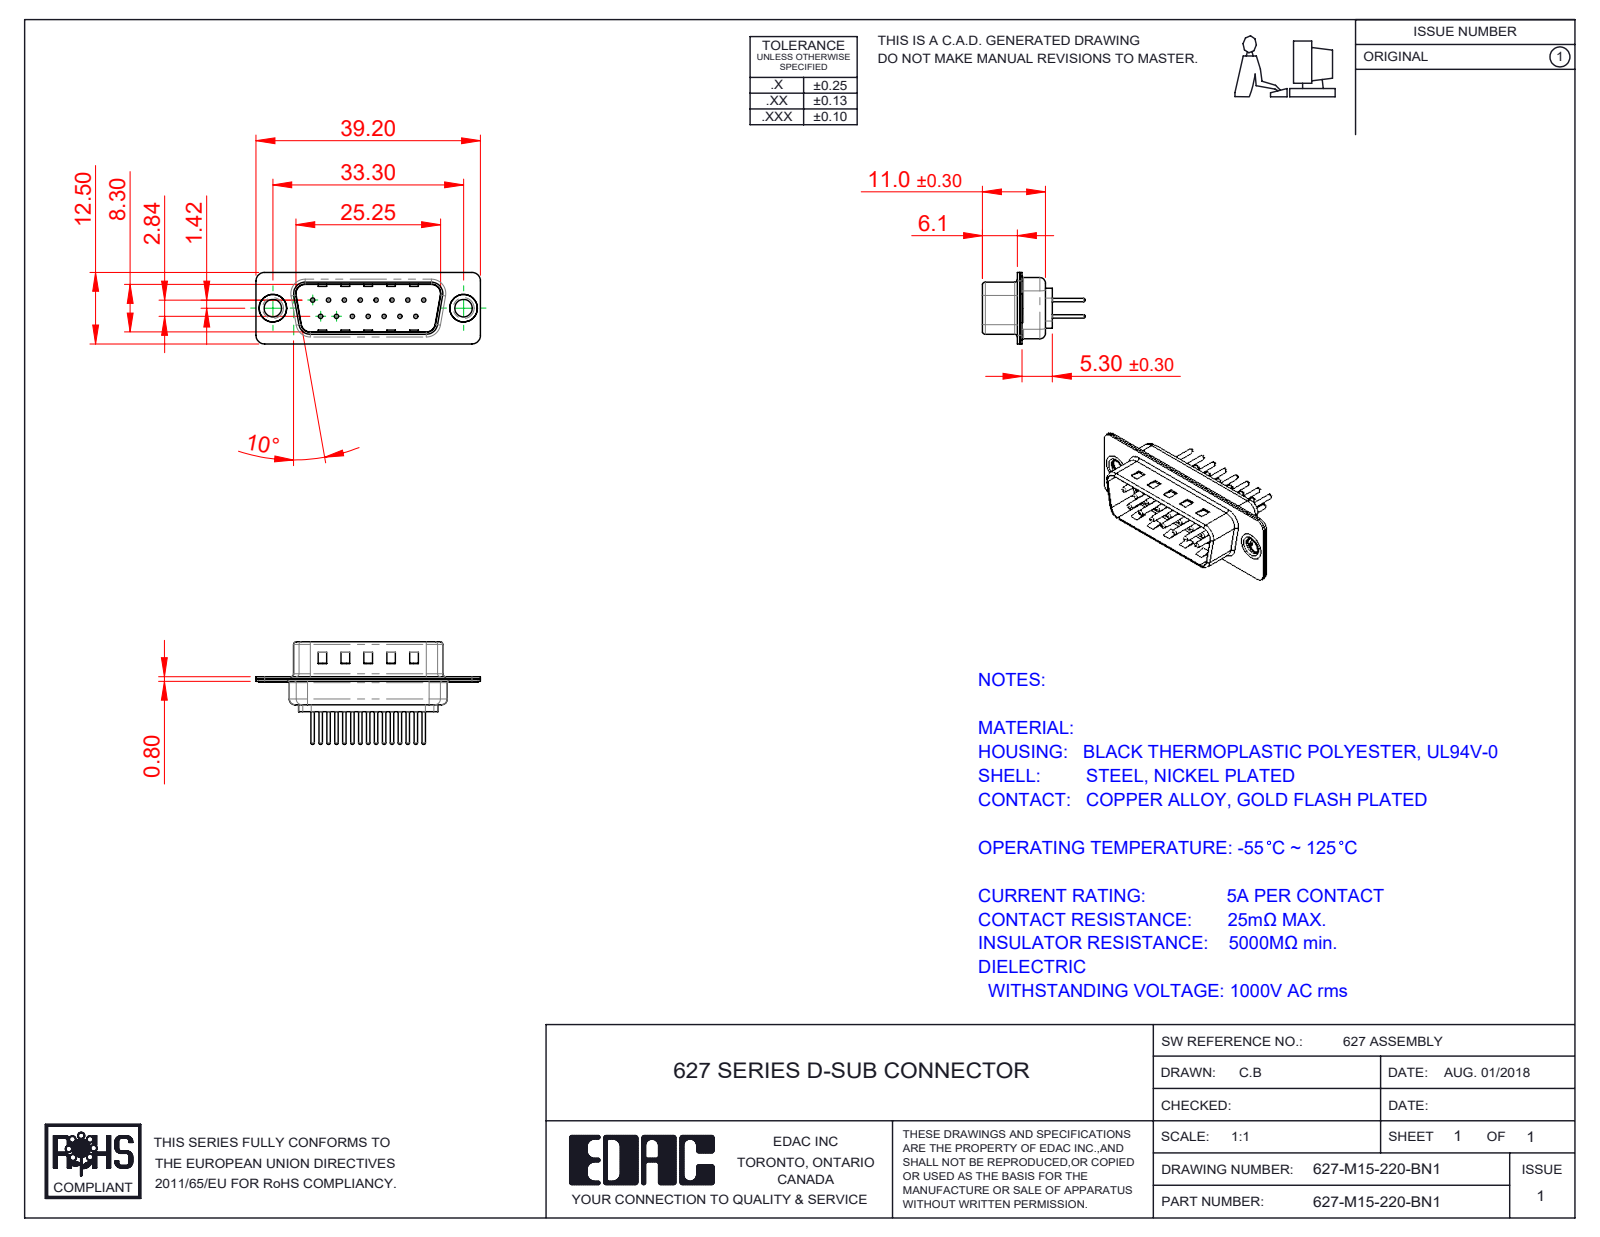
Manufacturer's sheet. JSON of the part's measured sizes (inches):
{"part_name": "627-M15-220-BN1; 627M Shell Front_15 Contacts; 627M Shell Rear_15 Contacts; 627M Contact Row 1_20 (+3 more)", "step_written_by": "SolidWorks 2020 (CONFIG_CONTROL_DESIGN)", "units": "inches", "bodies": {"solids": 20, "faces": 869, "planar": 244, "cylindrical": 327, "other": 298}, "overall_size": [1.543, 0.705, 0.492], "volume_in3": 0.108, "surface_area_in2": 7.228, "round_holes": [[0.03, 15], [0.063, 15], [0.079, 15], [0.12, 2], [0.157, 2], [0.189, 2]], "round_bosses_or_shafts": [[0.059, 15], [0.024, 15], [0.197, 2], [0.193, 2], [0.14, 2]], "partial_cylinders_radius": [[0.059, 16], [0.079, 12], [0.02, 8], [0.063, 8], [0.01, 4], [0.024, 4], [0.026, 4], [0.035, 4]], "face_to_face_distances": [0.016, 0.031, 0.374, 0.358, 0.343, 0.39, 0.047, 0.24, 0.224, 0.209], "hole_center_spacings": [0.124, 0.109, 0.218, 0.327, 0.436, 0.198, 0.198, 0.294]}
